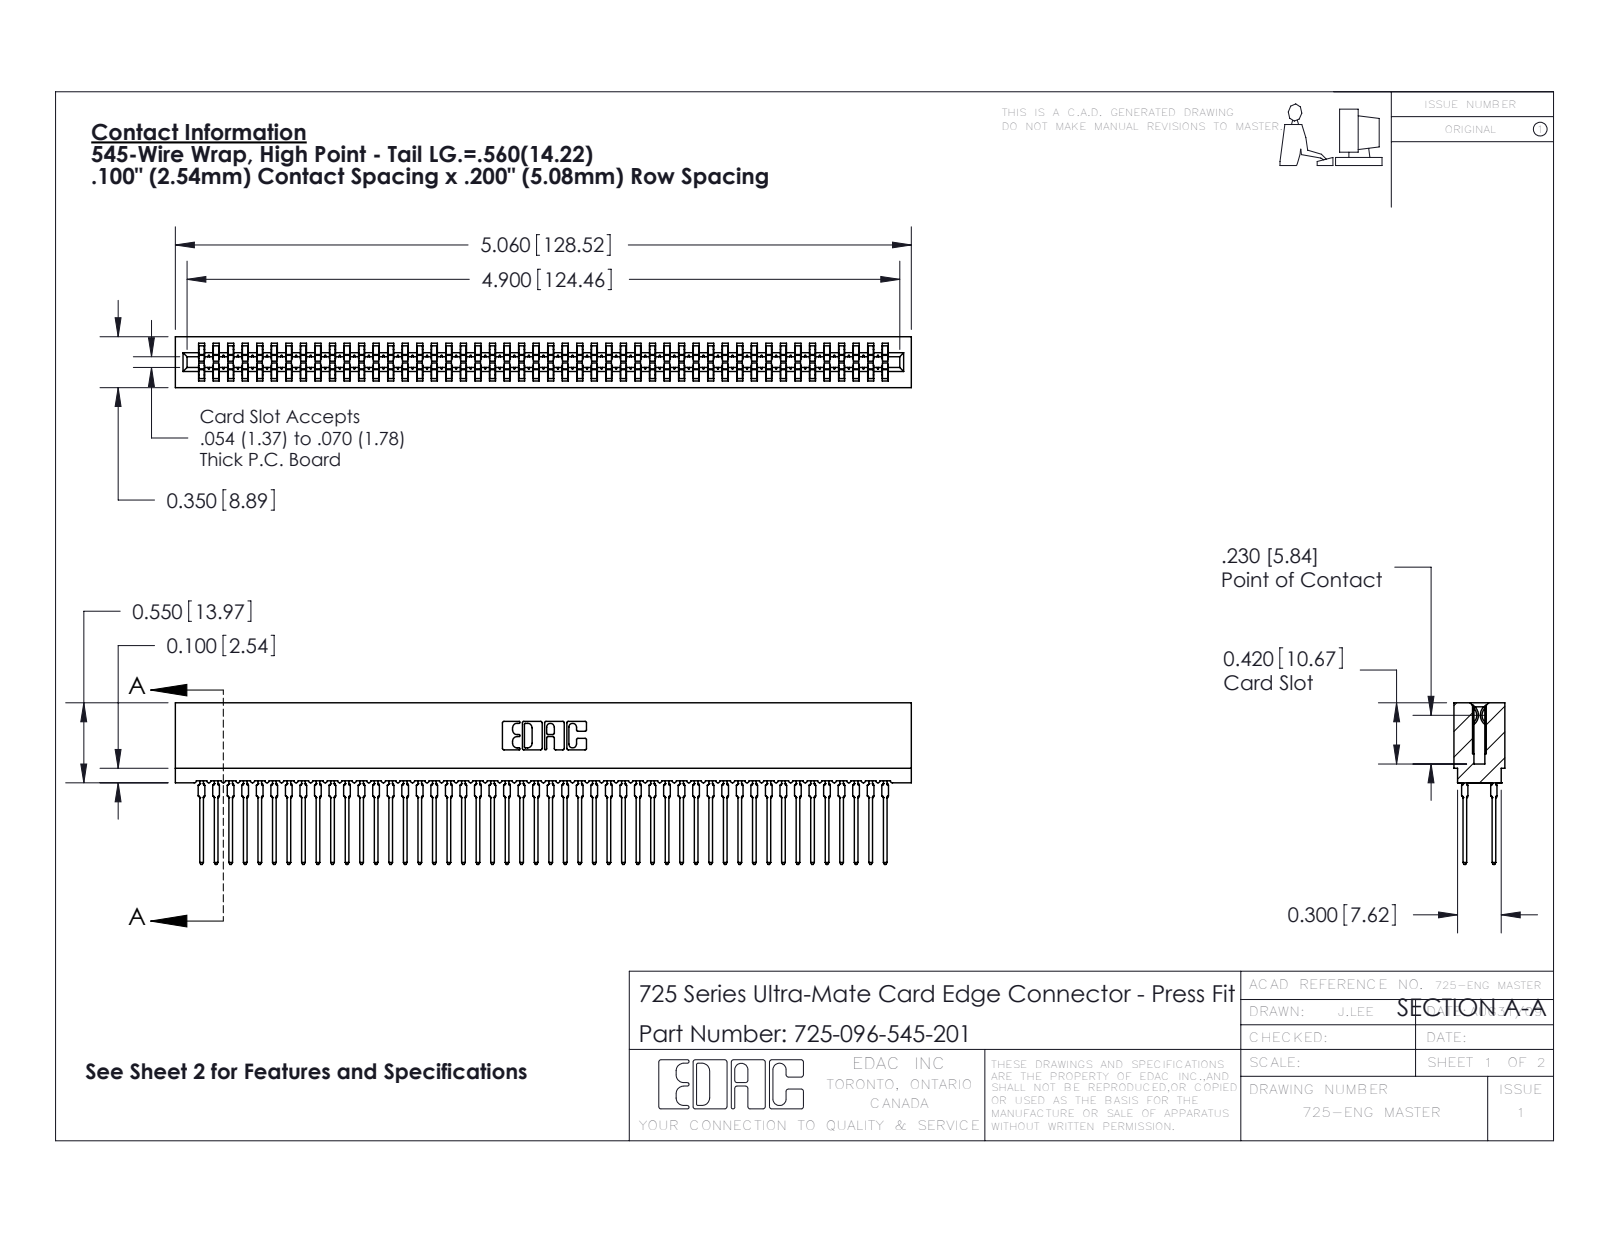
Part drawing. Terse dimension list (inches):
name: 745-292-001_545; 725-096-545-201; 725 Part_Insulator Option - 01
written by: SolidWorks 2016 (CONFIG_CONTROL_DESIGN)
unit: in
bodies: 97 solids, 8687 faces (4471 planar, 1720 cylindrical, 2496 other)
size: 5.06 × 1.11 × 0.35
volume: 0.641 in³; area: 36.84 in²
rounds: 192× R0.021, 96× R0.015, 22× R0.01, 8× R0.005, 8× R0.011, 6× R0.007, 6× R0.031, 3× R0.026
face distances: 0.2, 0.063, 0.287, 0.35, 0.212, 0.138, 0.076, 0.149, 0.087, 0.263
